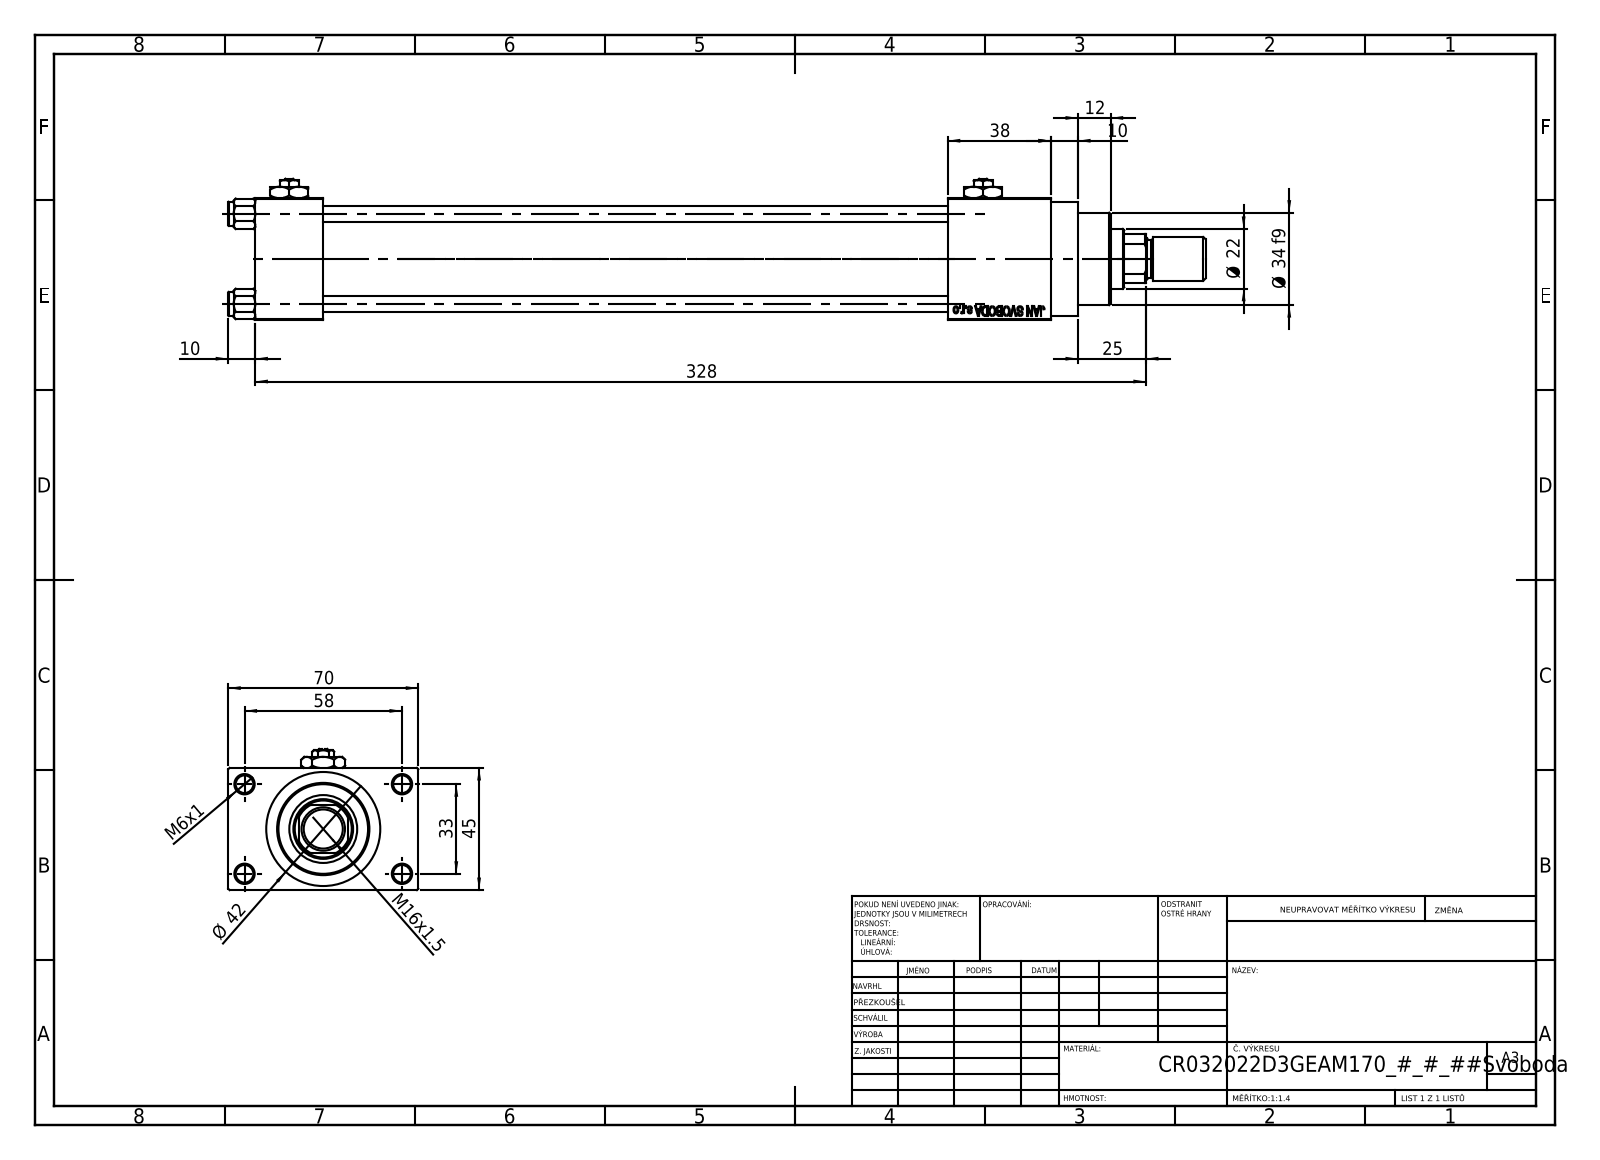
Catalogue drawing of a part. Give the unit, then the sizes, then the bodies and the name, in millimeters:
Units: millimetres
Overall size (bounding box): 360 × 70 × 52
Round holes (diameter × count): ⌀6 ×4, ⌀6.5 ×4, ⌀7 ×2, ⌀13.16 ×2, ⌀20 ×2, ⌀10.5 ×1, ⌀22 ×1, ⌀24 ×1, ⌀25 ×1, ⌀32 ×1, ⌀33 ×1
Round bosses / shafts (diameter × count): ⌀9 ×4, ⌀42 ×1, ⌀38 ×1, ⌀34 ×1, ⌀16 ×1, ⌀14 ×1
Partial cylindrical surfaces — rounded edges, fillets, slot ends (radius × count): R10.5 ×1
Main face-to-face distances: 45, 25, 12.5, 57.5, 230, 255, 268, 38, 70, 293
Hole centre spacings: 12.4, 23.48, 33.2, 33.37, 35.35, 45.6, 56.35, 33
Volume: 395 835 mm³ · Surface area: 148 337 mm²
Bodies: 14 solids, 1216 faces (546 planar, 104 cylindrical, 566 other)
Part name (STEP PRODUCT): V215CR_VCP_D; V215_VC_A; Zatka_pro_OIL_PORT; NUT_M5_D (+3 more)
STEP written by: SolidWorks 2019 (CONFIG_CONTROL_DESIGN)
